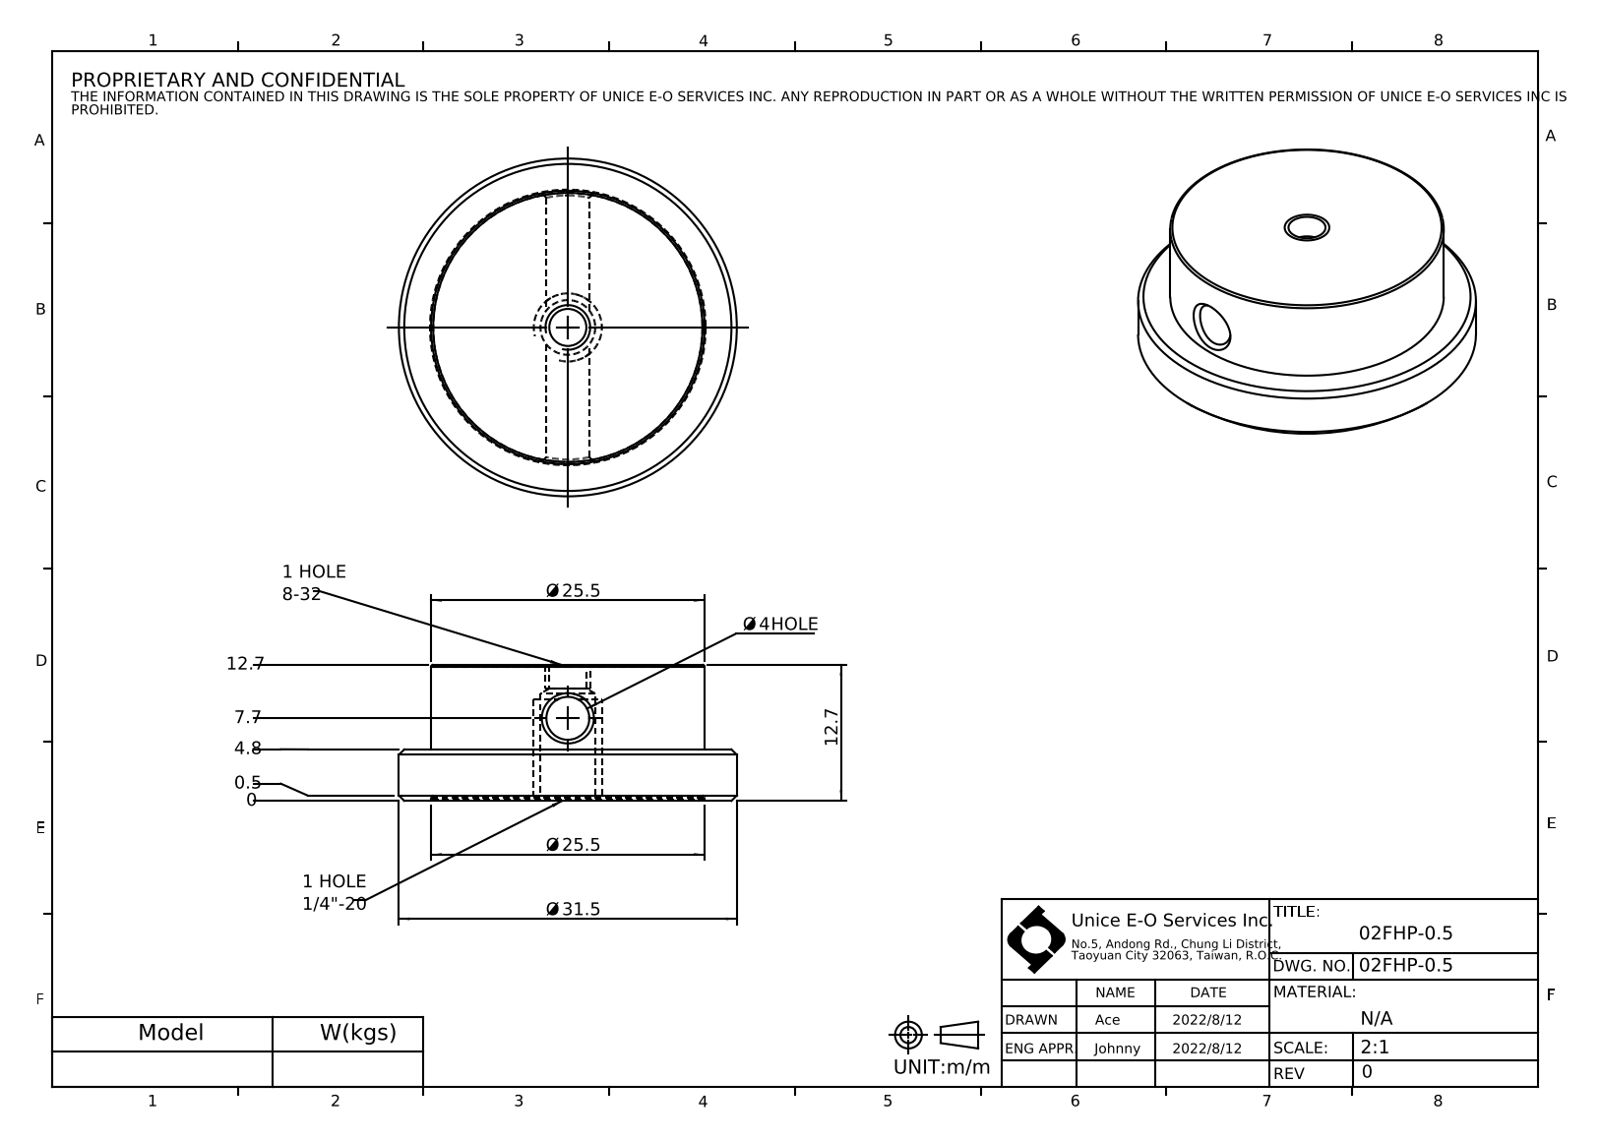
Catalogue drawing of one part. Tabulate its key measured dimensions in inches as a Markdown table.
| quantity | value |
| --- | --- |
| part name | 02FHP-0.5 |
| STEP written by | SolidWorks 2021 (CONFIG_CONTROL_DESIGN) |
| units | inches |
| bodies | 1 solid, 34 faces (4 planar, 14 cylindrical, 16 other) |
| overall size | 1.24 × 1.24 × 0.5 |
| volume | 0.428 in³ |
| surface area | 4.645 in² |
| round holes (diameter × count) | 0.136 × 1, 0.157 × 1, 0.201 × 1, 1.004 × 1 |
| round bosses / shafts (diameter × count) | 1.24 × 1 |
| main face-to-face distances | 0.48, 0.169, 0.311, 0.02, 0.189, 0.5 |
